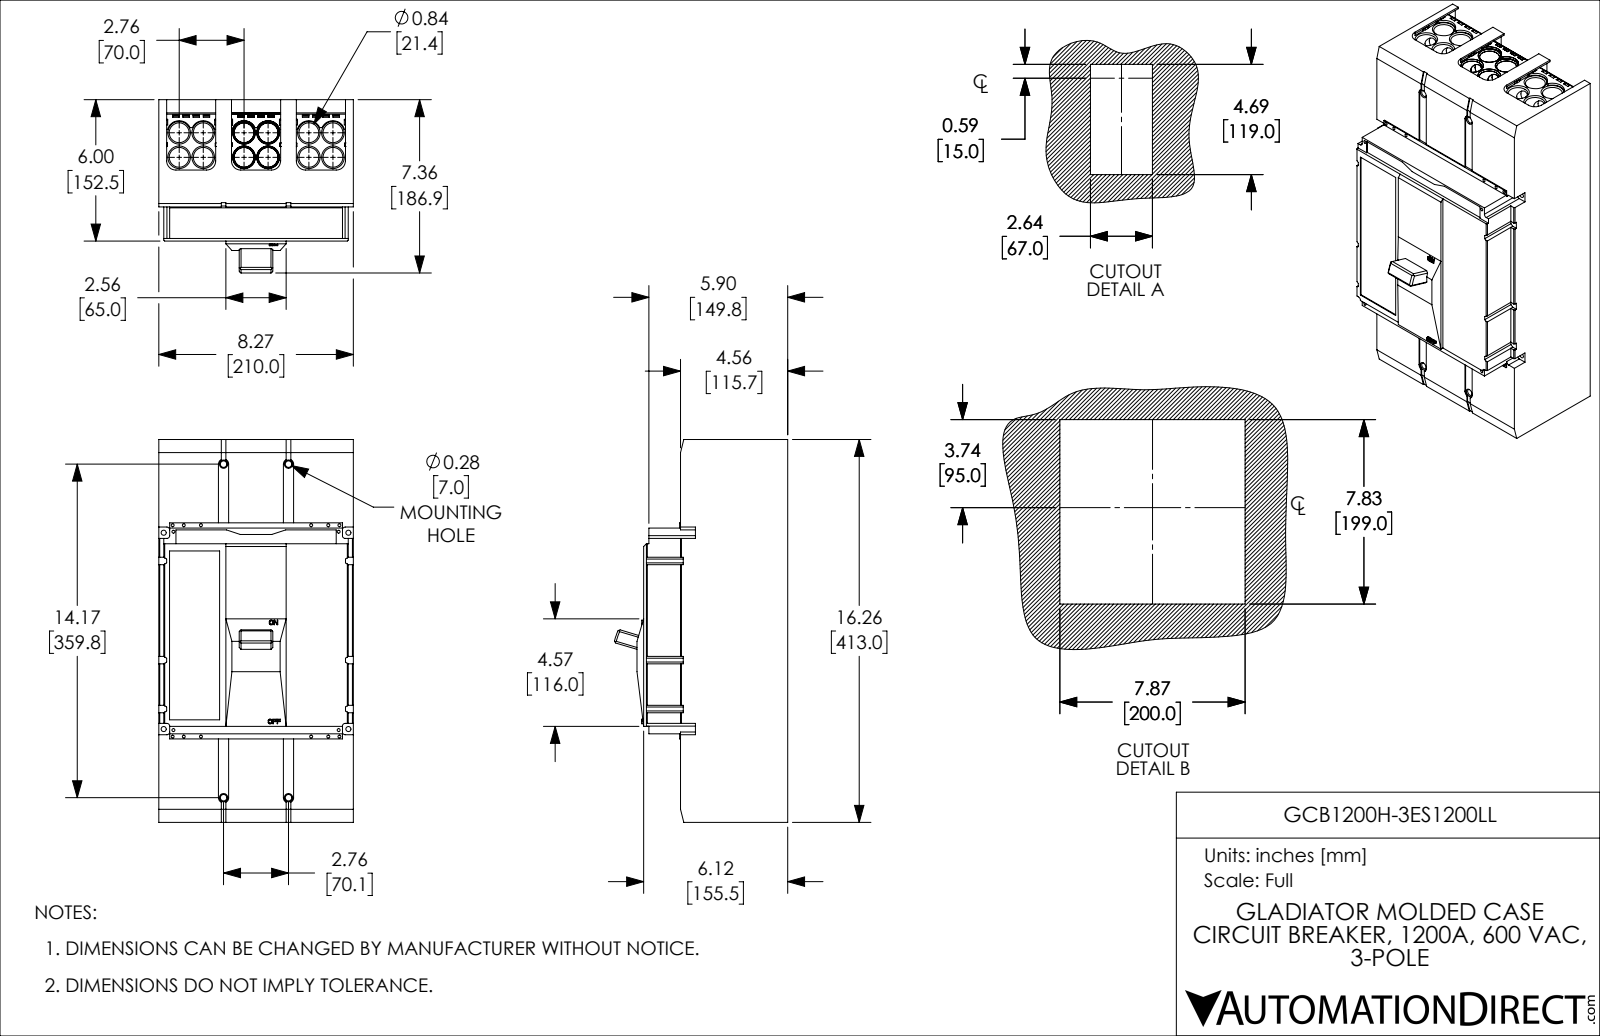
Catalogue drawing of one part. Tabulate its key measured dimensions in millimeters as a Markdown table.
| quantity | value |
| --- | --- |
| part name | GCB1200H-3ES1200LL |
| STEP written by | SolidWorks 2021 (CONFIG_CONTROL_DESIGN) |
| units | millimeters |
| bodies | 17 solids, 3613 faces (1270 planar, 1437 cylindrical, 906 other) |
| overall size | 413 × 210 × 186.9 |
| volume | 11 440 000 mm³ |
| surface area | 892 300 mm² |
| round holes (diameter × count) | 17 × 24, 17.8 × 24, 3.2 × 16, 10.8 × 12, 21.4 × 12, 24.2 × 12, 5.5 × 4, 7 × 4, 5.2 × 2 |
| partial cylindrical surfaces (radius × count) | 0.5 × 64, 1 × 24, 1.5 × 20, 2 × 12, 10 × 6, 13 × 6, 2.9 × 4, 3 × 4 |
| main face-to-face distances | 4, 70, 210, 132, 66, 74, 58, 17.2, 136, 78 |
| hole center spacings | 26, 70, 74.9, 26.5, 37.1, 228, 7.1, 10.6 |
